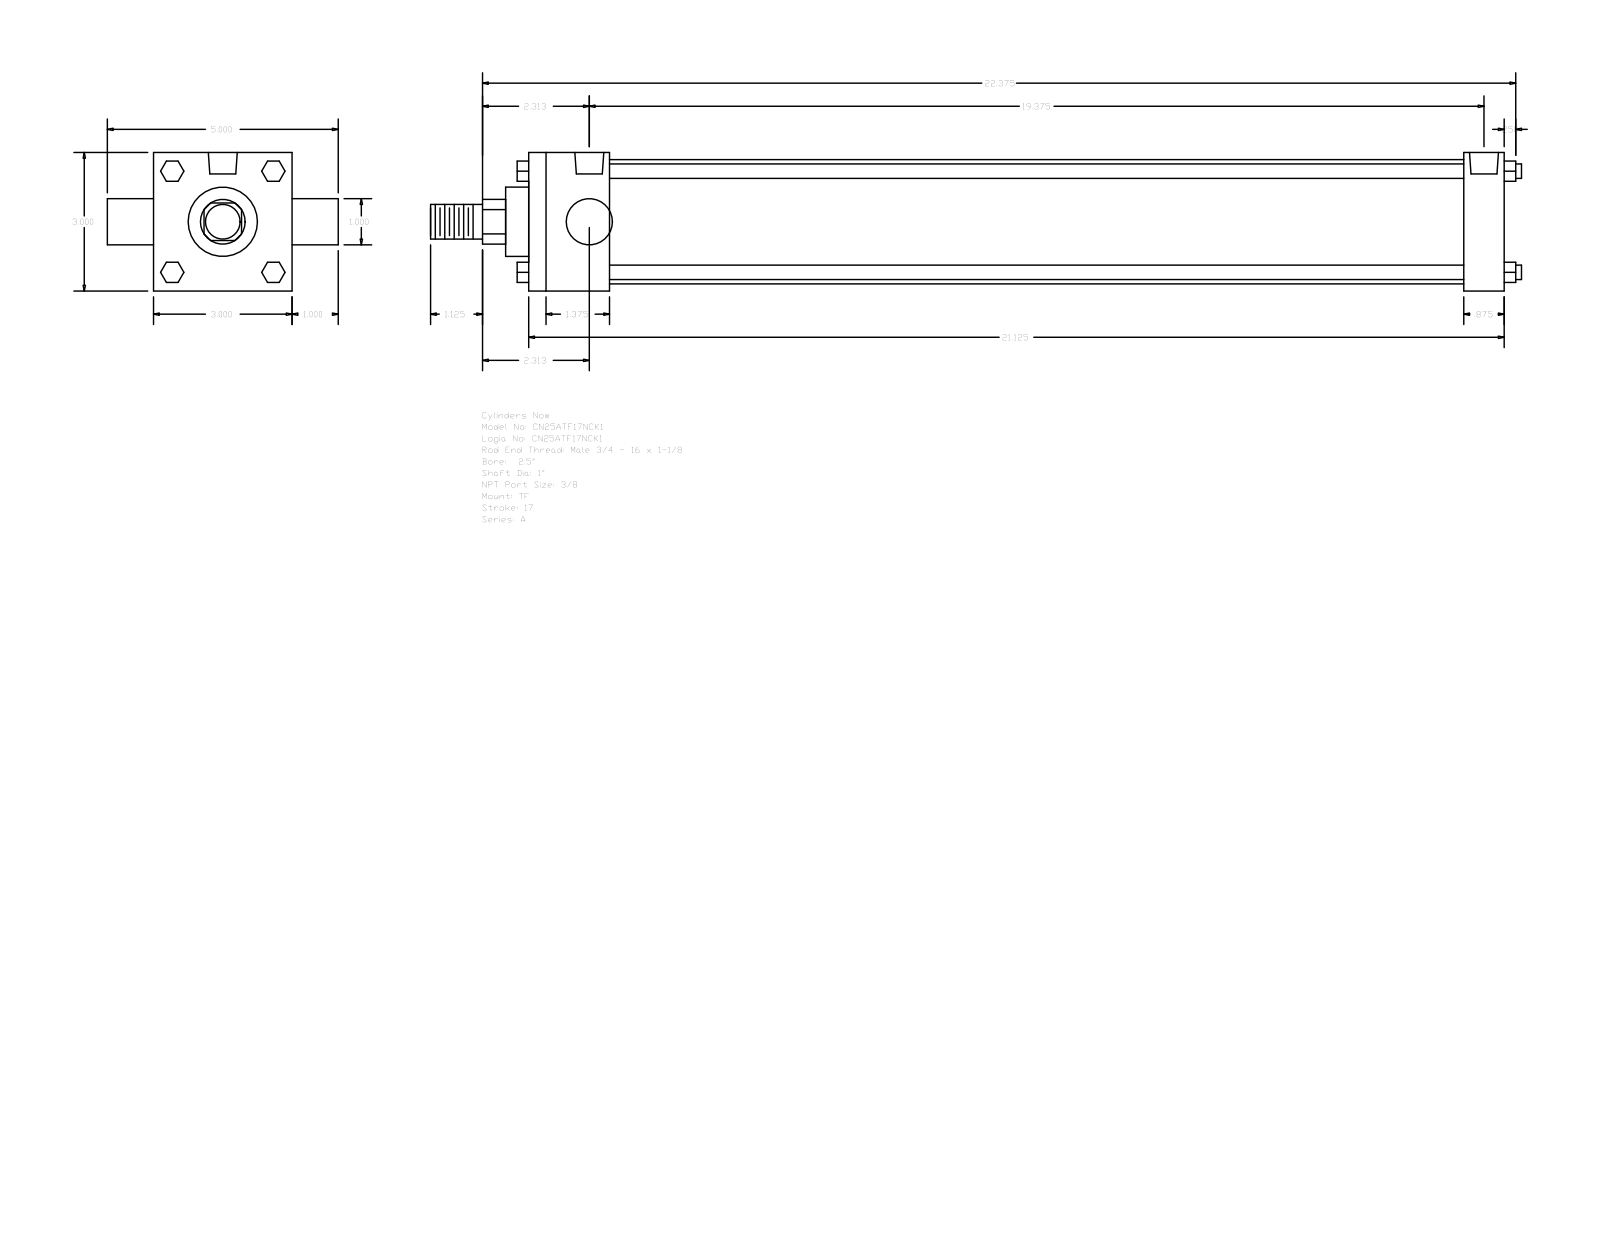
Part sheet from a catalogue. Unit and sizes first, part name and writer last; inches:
Units: inches
Overall size (bounding box): 23.625 × 5 × 3
Round holes (diameter × count): ⌀0.219 ×3, ⌀0.627 ×2
Round bosses / shafts (diameter × count): ⌀0.313 ×4, ⌀1 ×2, ⌀2.69 ×1, ⌀1.5 ×1, ⌀0.75 ×1
Partial cylindrical surfaces — rounded edges, fillets, slot ends (radius × count): R0.484 ×1
Main face-to-face distances: 3, 21.125, 1.75, 20.25, 18.5, 19.375, 0.875, 1, 4, 21.625
Hole centre spacings: 0.094, 19.469, 19.375, 19.562
Bodies: 0 solids, 120 faces (92 planar, 28 cylindrical, 0 other)
Part name (STEP PRODUCT): A_TF__0250_1
STEP written by: GSSL Pune (CONFIG_CONTROL_DESIGN)
